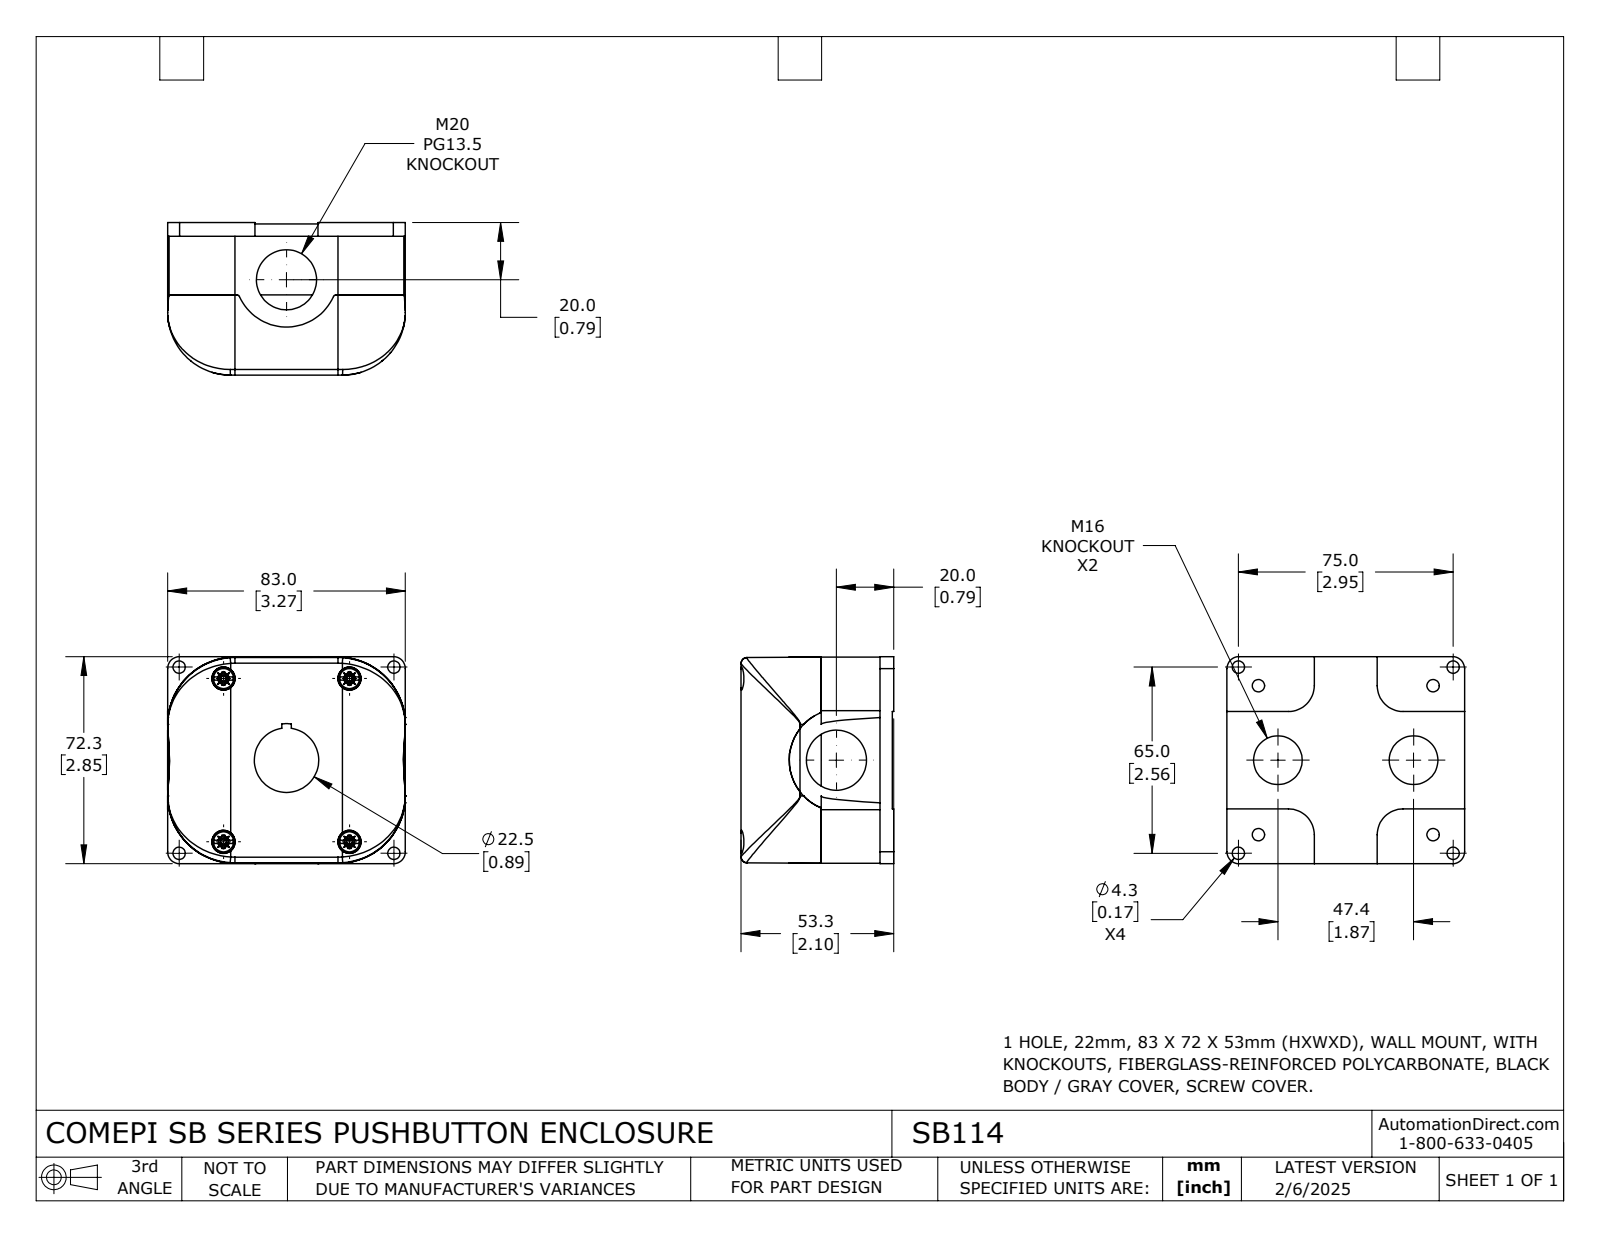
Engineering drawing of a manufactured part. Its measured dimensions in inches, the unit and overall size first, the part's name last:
Units: inches
Overall size (bounding box): 3.268 × 2.846 × 2.098
Round holes (diameter × count): ⌀0.169 ×8, ⌀0.323 ×4, ⌀0.669 ×2, ⌀0.827 ×2
Round bosses / shafts (diameter × count): ⌀0.276 ×4
Partial cylindrical surfaces — rounded edges, fillets, slot ends (radius × count): R0.035 ×4, R0.079 ×4, R0.354 ×4, R0.38 ×4, R0.925 ×4, R0.709 ×2, R0.835 ×2, R0.866 ×2
Main face-to-face distances: 0.976, 0.878, 0.098, 2.079, 1.98, 1.102, 0.118, 0.02, 0.996, 2.098
Hole centre spacings: 0.376, 1.058, 1.39, 2.32, 2.367, 2.689, 2.728, 3.531
Volume: 12.51 in³ · Surface area: 79.33 in²
Bodies: 2 solids, 463 faces (273 planar, 114 cylindrical, 76 other)
Part name (STEP PRODUCT): SB114
STEP written by: SolidWorks 2024 (CONFIG_CONTROL_DESIGN)
